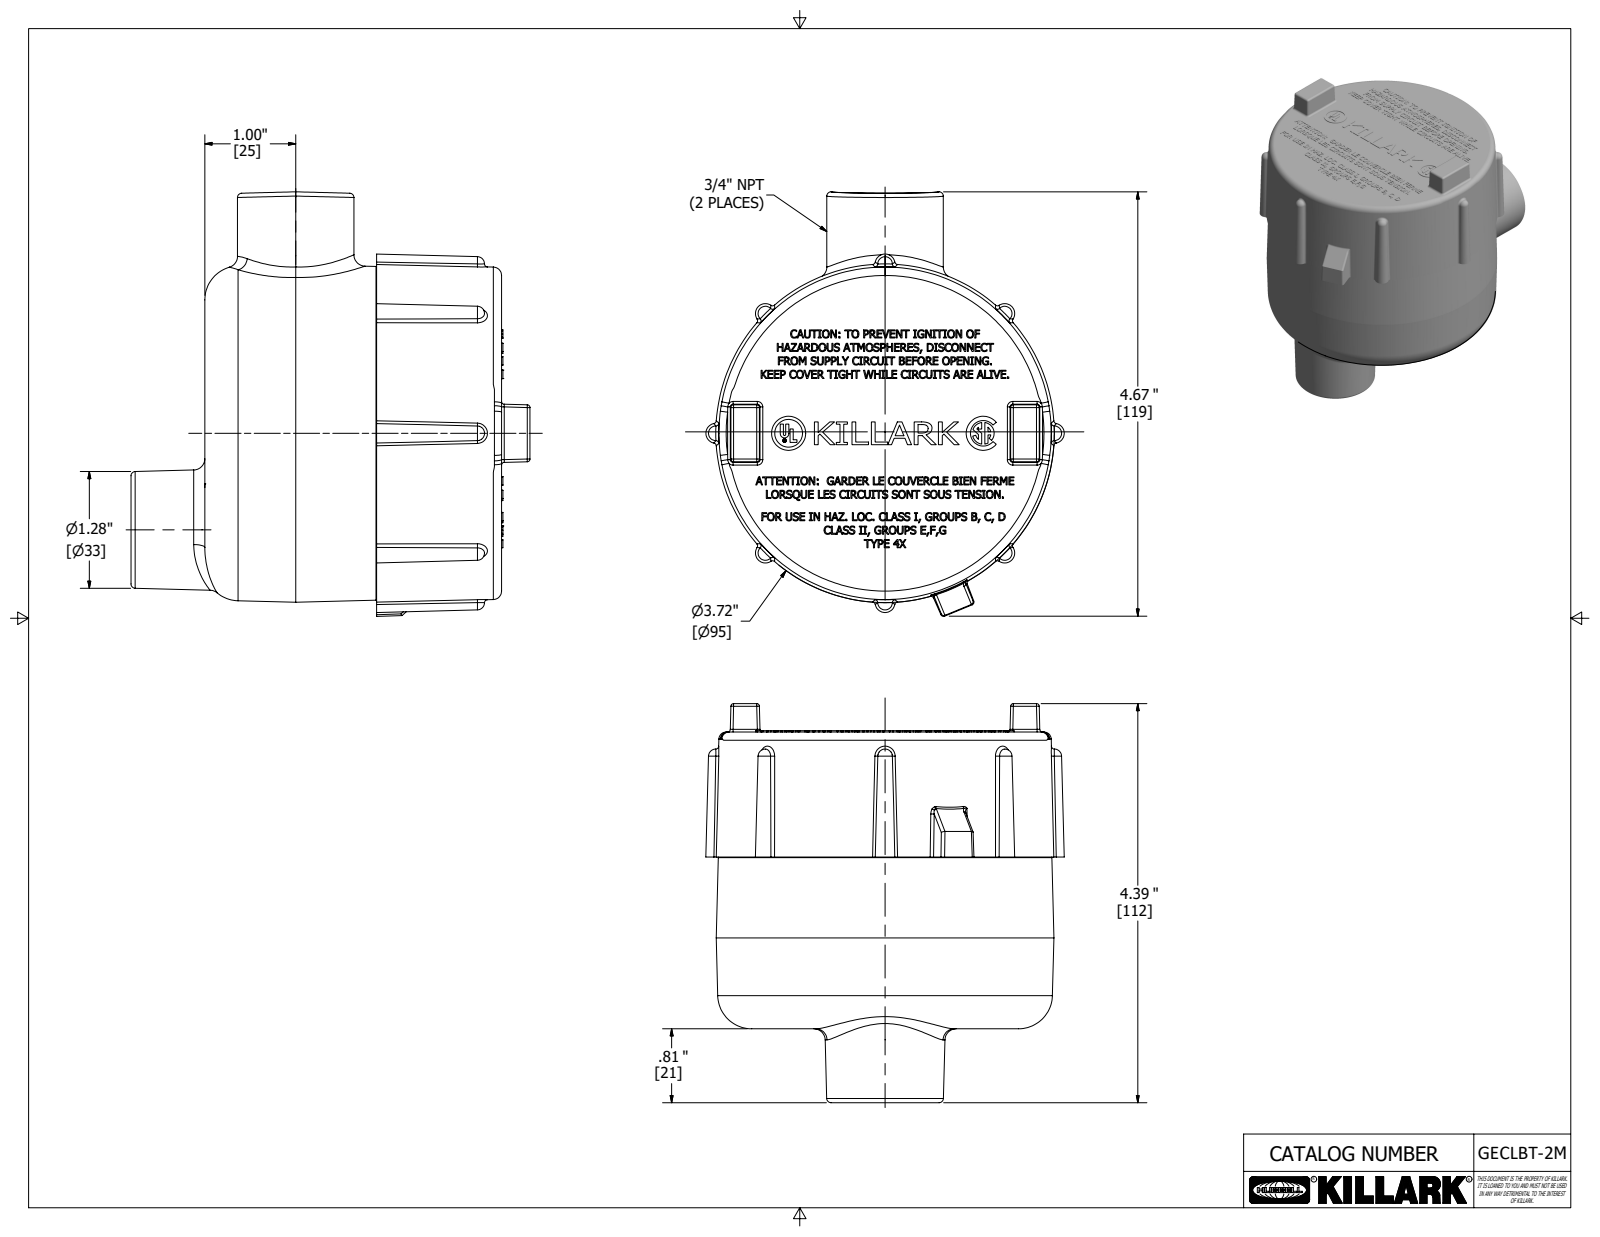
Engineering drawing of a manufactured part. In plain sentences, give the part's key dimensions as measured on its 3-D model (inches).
The part is named "GECLBT-2; 13418-4; 18476-1". Its 3-D file was written by "Autodesk Inventor 2020 (AUTOMOTIVE_DESIGN)". It is 2 solids with 5088 faces: 3016 planar, 127 cylindrical and 1945 other. Overall it measures 4.671 by 4.39 by 3.944 inches. Its volume is 17.02 cubic inches and its surface area 140.1 square inches. Round holes: 2 of diameter 0.792, 1 of diameter 0.035, 1 of diameter 0.145, 1 of diameter 0.187, 1 of diameter 0.306. Round bosses or shafts: 1 of diameter 3.187, 1 of diameter 3.06, 1 of diameter 1.281, 1 of diameter 0.375, 1 of diameter 0.042. Partial cylindrical surfaces (rounded edges, fillets, slot ends): 20 of radius 0.03, 8 of radius 0.031, 1 of radius 0.004, 1 of radius 0.007, 1 of radius 0.012, 1 of radius 0.047, 1 of radius 0.085, 1 of radius 0.12. The main face-to-face distances are 0.344, 2.702, 3.046, 1.671, 1.031, 1.375, 0.219, 1.89, 2.921, 3.265. The hole center spacings are 0.092, 1.48, 1.502, 1.961, 1.962, 2.033.
